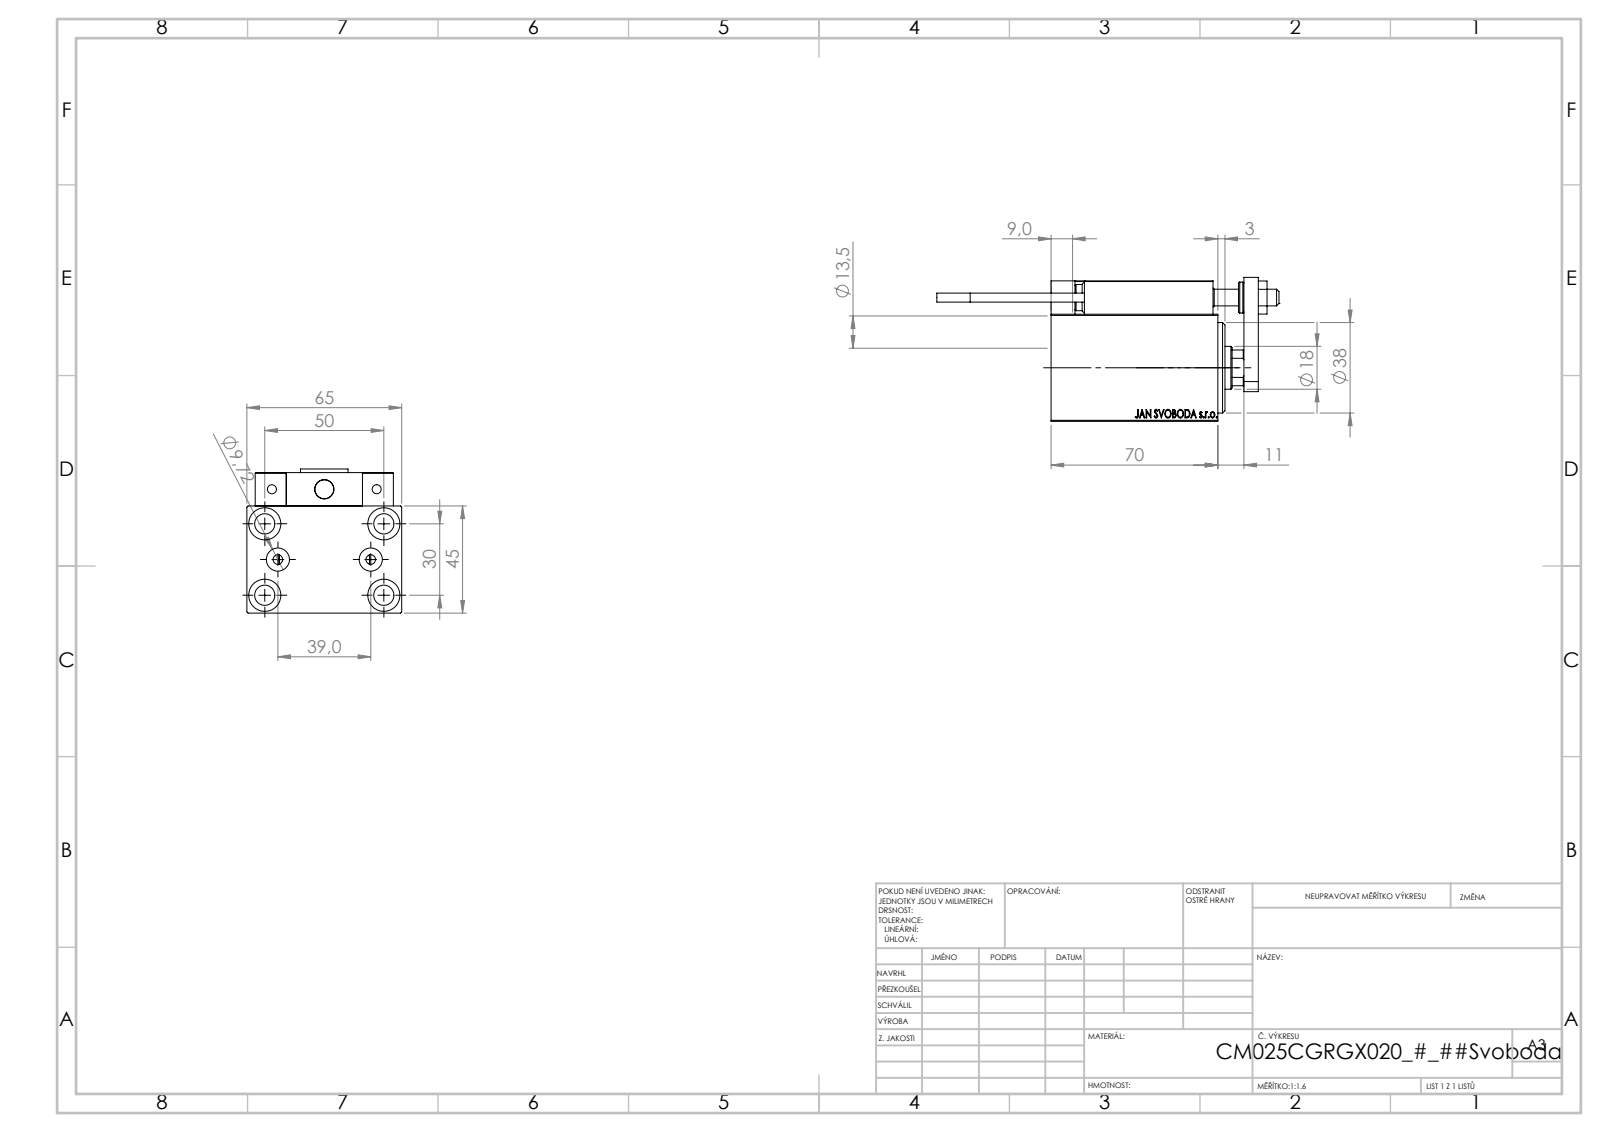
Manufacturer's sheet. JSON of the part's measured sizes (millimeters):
{"part_name": "KONCOVKA; V450CM_C_Body; ZARAZKA; MAGNET (+7 more)", "step_written_by": "SolidWorks 2019 (CONFIG_CONTROL_DESIGN)", "units": "millimeters", "bodies": {"solids": 23, "faces": 1278, "planar": 560, "cylindrical": 184, "other": 534}, "overall_size": [143.7, 65, 60.5], "volume_mm3": 223993, "surface_area_mm2": 69960, "round_holes": [[4, 6], [8, 5], [8.5, 5], [3.2, 4], [13.5, 4], [5, 2], [9.72, 2], [7, 1], [14.5, 1], [18, 1], [21.5, 1], [25, 1]], "round_bosses_or_shafts": [[5, 2], [3.8, 2], [13, 1], [11, 1]], "partial_cylinders_radius": [[0.3, 30], [3, 2], [8.5, 1]], "face_to_face_distances": [45, 65, 59, 14, 6, 3, 19, 5, 7, 20], "hole_center_spacings": [15.98, 29.15, 46.96, 11.37, 19.5, 20, 22.09, 28.9]}
